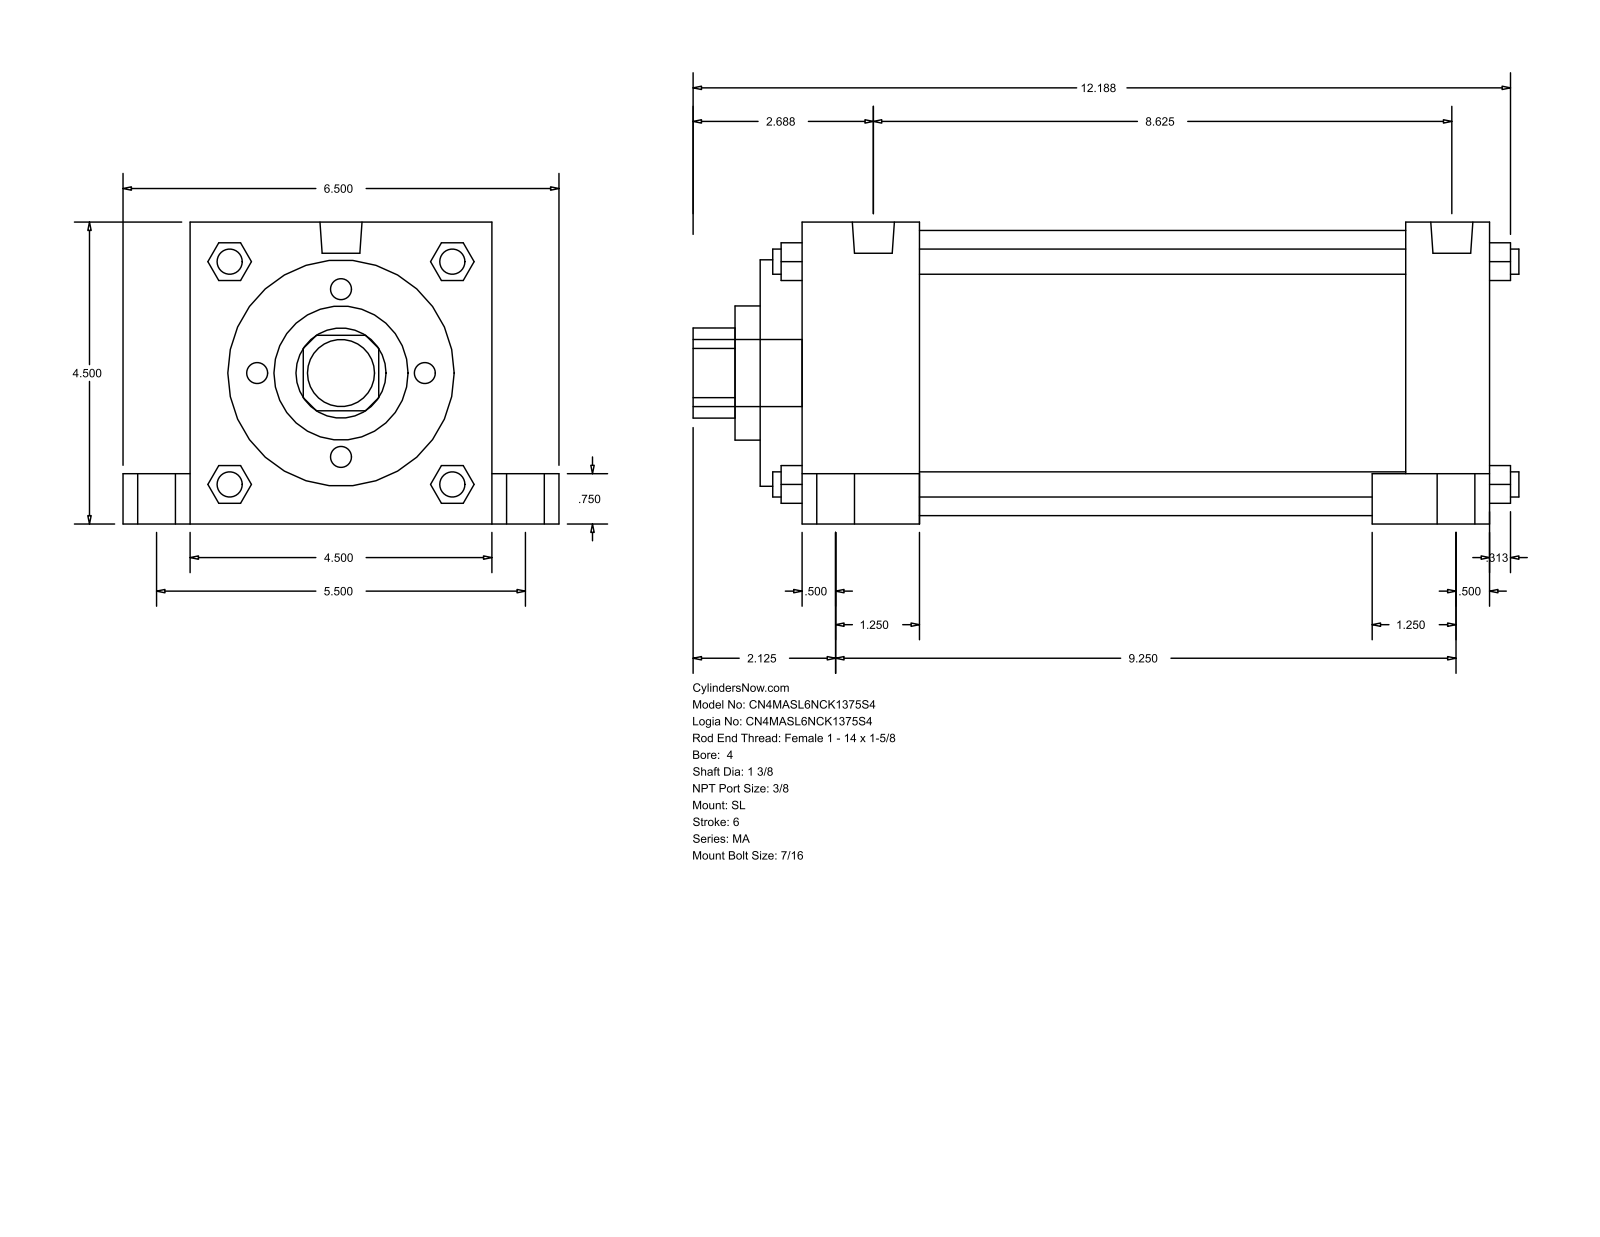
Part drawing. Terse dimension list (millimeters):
name: MA_SL__0400_1.375
written by: GSSL Pune (CONFIG_CONTROL_DESIGN)
unit: mm
bodies: 0 solids, 150 faces (113 planar, 37 cylindrical, 0 other)
size: 312.74 × 165.1 × 114.3
holes: 1× ⌀34.92, 1× ⌀50.8, 1× ⌀85.72, 1× ⌀107.95
bosses: 4× ⌀20.64, 4× ⌀14.29, 4× ⌀11.11, 4× ⌀9.53, 2× ⌀15.93, 1× ⌀25.4
rounds: 1× R17.06
face distances: 114.3, 260.35, 276.22, 15.87, 60.32, 44.45, 215.9, 244.48, 228.61, 184.16
